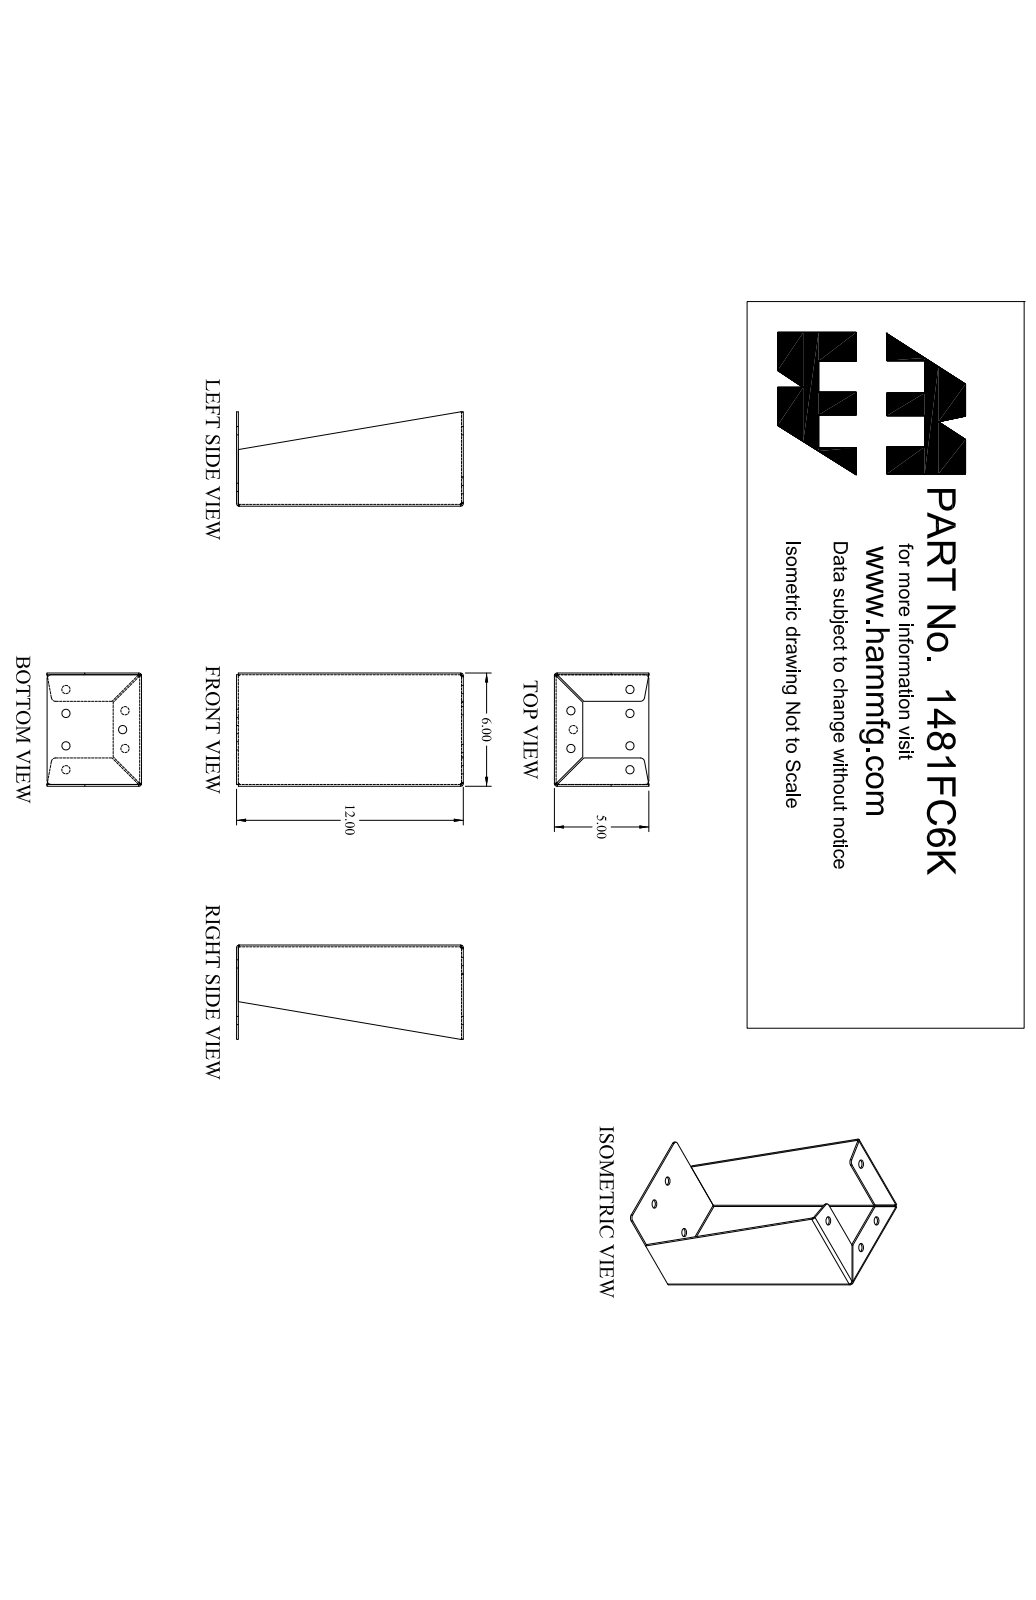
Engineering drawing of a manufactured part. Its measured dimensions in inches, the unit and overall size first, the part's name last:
Units: inches
Overall size (bounding box): 12 × 6 × 5
Round holes (diameter × count): ⌀0.437 ×7
Partial cylindrical surfaces — rounded edges, fillets, slot ends (radius × count): R0.048 ×6, R0.143 ×6, R0.22 ×4
Main face-to-face distances: 0.095, 5.905, 5.81, 6, 0.095, 11.81, 11.905, 11.905, 12, 1.405
Hole centre spacings: 1.008, 3.12, 3.128, 3.321, 3.636, 4.419, 1.266, 1.266
Volume: 19.77 in³ · Surface area: 423.3 in²
Bodies: 1 solid, 78 faces (42 planar, 30 cylindrical, 6 other)
Part name (STEP PRODUCT): 1481FC6K_Default
STEP written by: SolidWorks 2019 (CONFIG_CONTROL_DESIGN)
